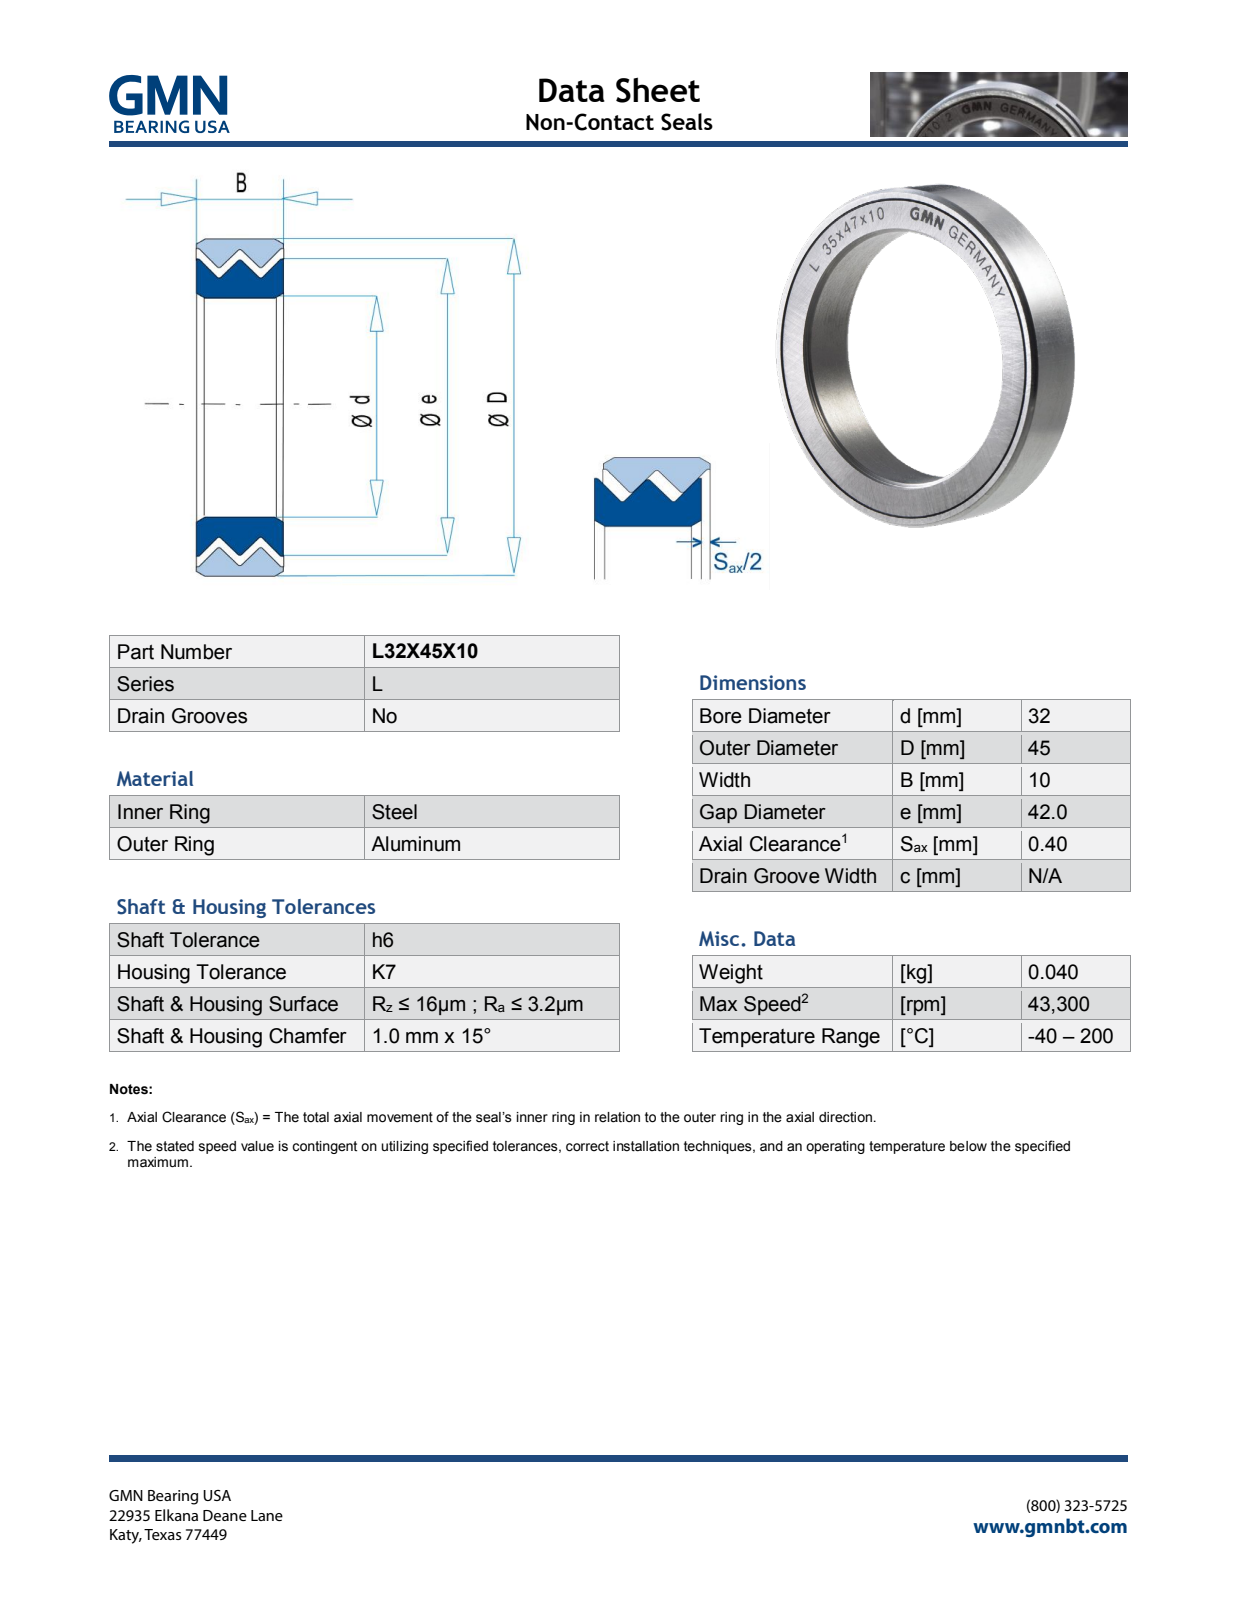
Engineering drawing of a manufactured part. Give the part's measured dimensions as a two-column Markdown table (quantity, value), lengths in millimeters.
| quantity | value |
| --- | --- |
| part name | L32X45X10_PRT |
| STEP written by | PRO/ENGINEER BY PARAMETRIC TECHNOLOGY CORPORATION, 2013150 (AUTOMOTIVE_DESIGN) |
| units | millimeters |
| bodies | 2 solids, 565 faces (509 planar, 12 cylindrical, 44 other) |
| overall size | 45 × 45 × 10.07 |
| volume | 7 487 mm³ |
| surface area | 7 128 mm² |
| round holes (diameter × count) | 32 × 1, 42.28 × 1 |
| round bosses / shafts (diameter × count) | 45 × 1, 42 × 1 |
| main face-to-face distances | 10, 10.07, 0.31, 2.42, 2.12, 1.82, 2.02, 1.08, 2.43, 2.11 |
